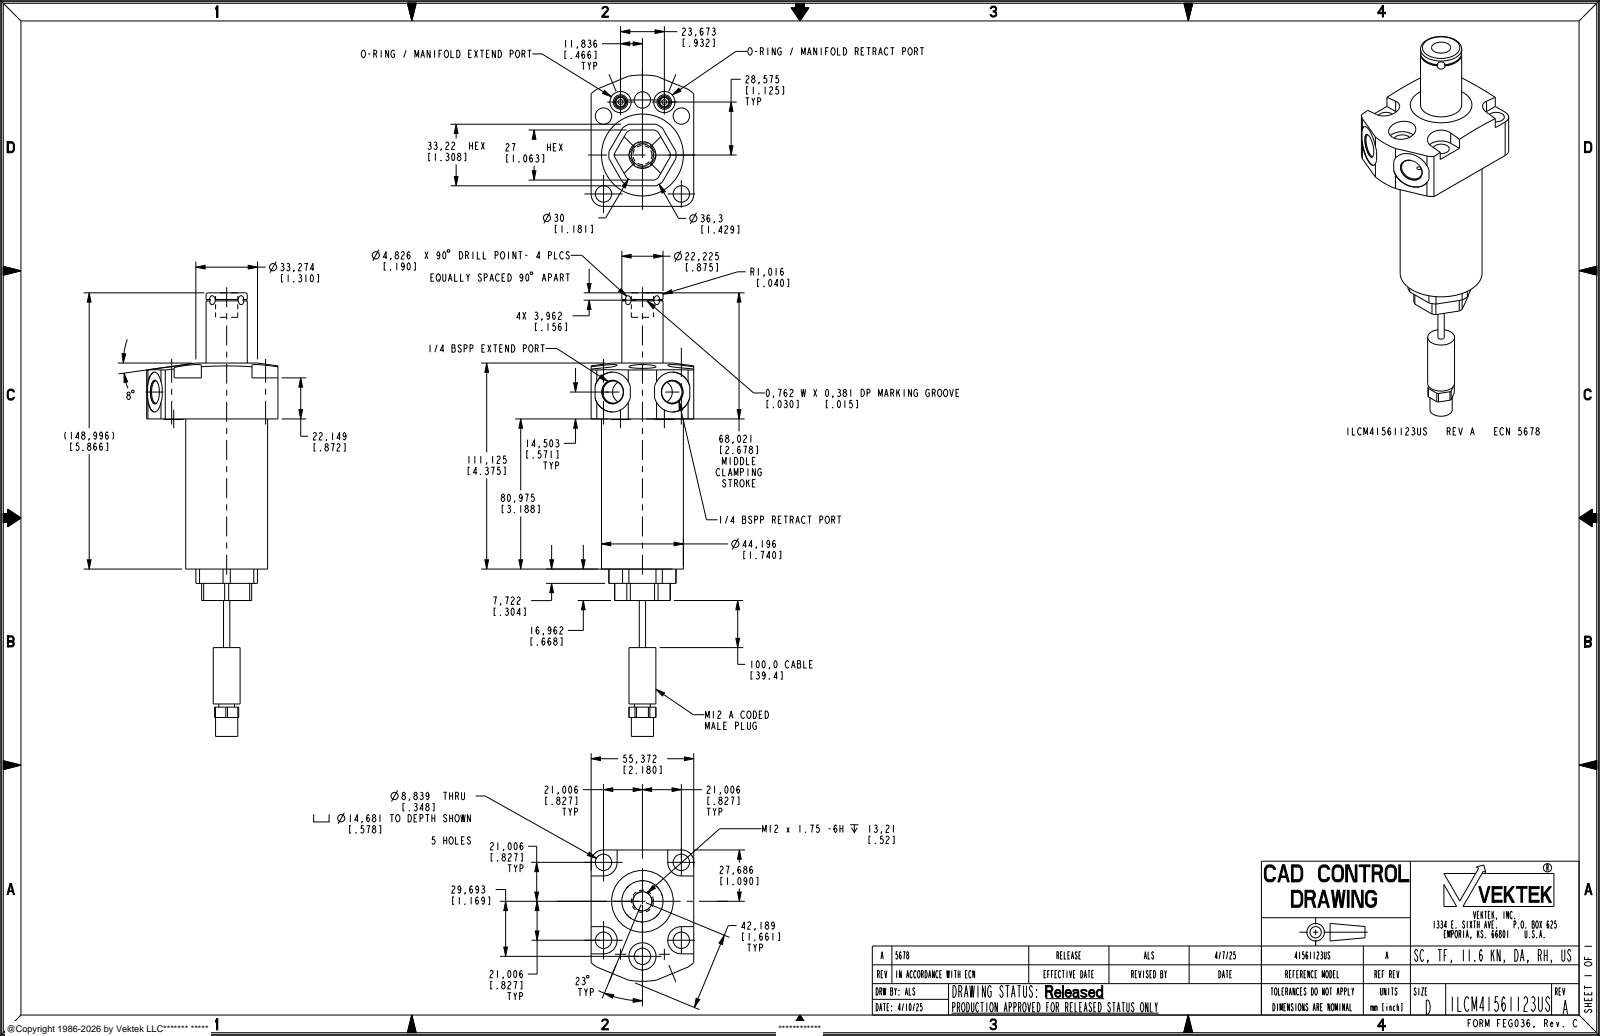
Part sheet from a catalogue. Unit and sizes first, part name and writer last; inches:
Units: inches
Overall size (bounding box): 9.42 × 3.04 × 2.38
Round holes (diameter × count): ⌀0.348 ×5, ⌀0.098 ×2, ⌀0.256 ×2, ⌀0.449 ×2, ⌀0.468 ×2, ⌀0.846 ×2, ⌀0.406 ×1, ⌀0.578 ×1, ⌀0.895 ×1
Round bosses / shafts (diameter × count): ⌀0.216 ×2, ⌀1.74 ×1, ⌀0.875 ×1, ⌀0.571 ×1, ⌀0.472 ×1, ⌀0.472 ×1, ⌀0.335 ×1, ⌀0.134 ×1
Partial cylindrical surfaces — rounded edges, fillets, slot ends (radius × count): R0.289 ×4, R0.255 ×2, R0.422 ×1, R0.591 ×1, R0.715 ×1, R1.7 ×1
Main face-to-face distances: 2.18, 3.188, 0.122, 1.185, 0.668, 3.856, 4.728, 4.06, 0.872, 5.043
Hole centre spacings: 1.17, 1.654, 0.468, 0.468, 0.895, 1.218, 1.327, 1.985
Volume: 15.17 in³ · Surface area: 60.69 in²
Bodies: 1 solid, 205 faces (88 planar, 87 cylindrical, 30 other)
Part name (STEP PRODUCT): ILCM41561123US
STEP written by: CREO PARAMETRIC BY PTC INC, 2021164 (AUTOMOTIVE_DESIGN)
